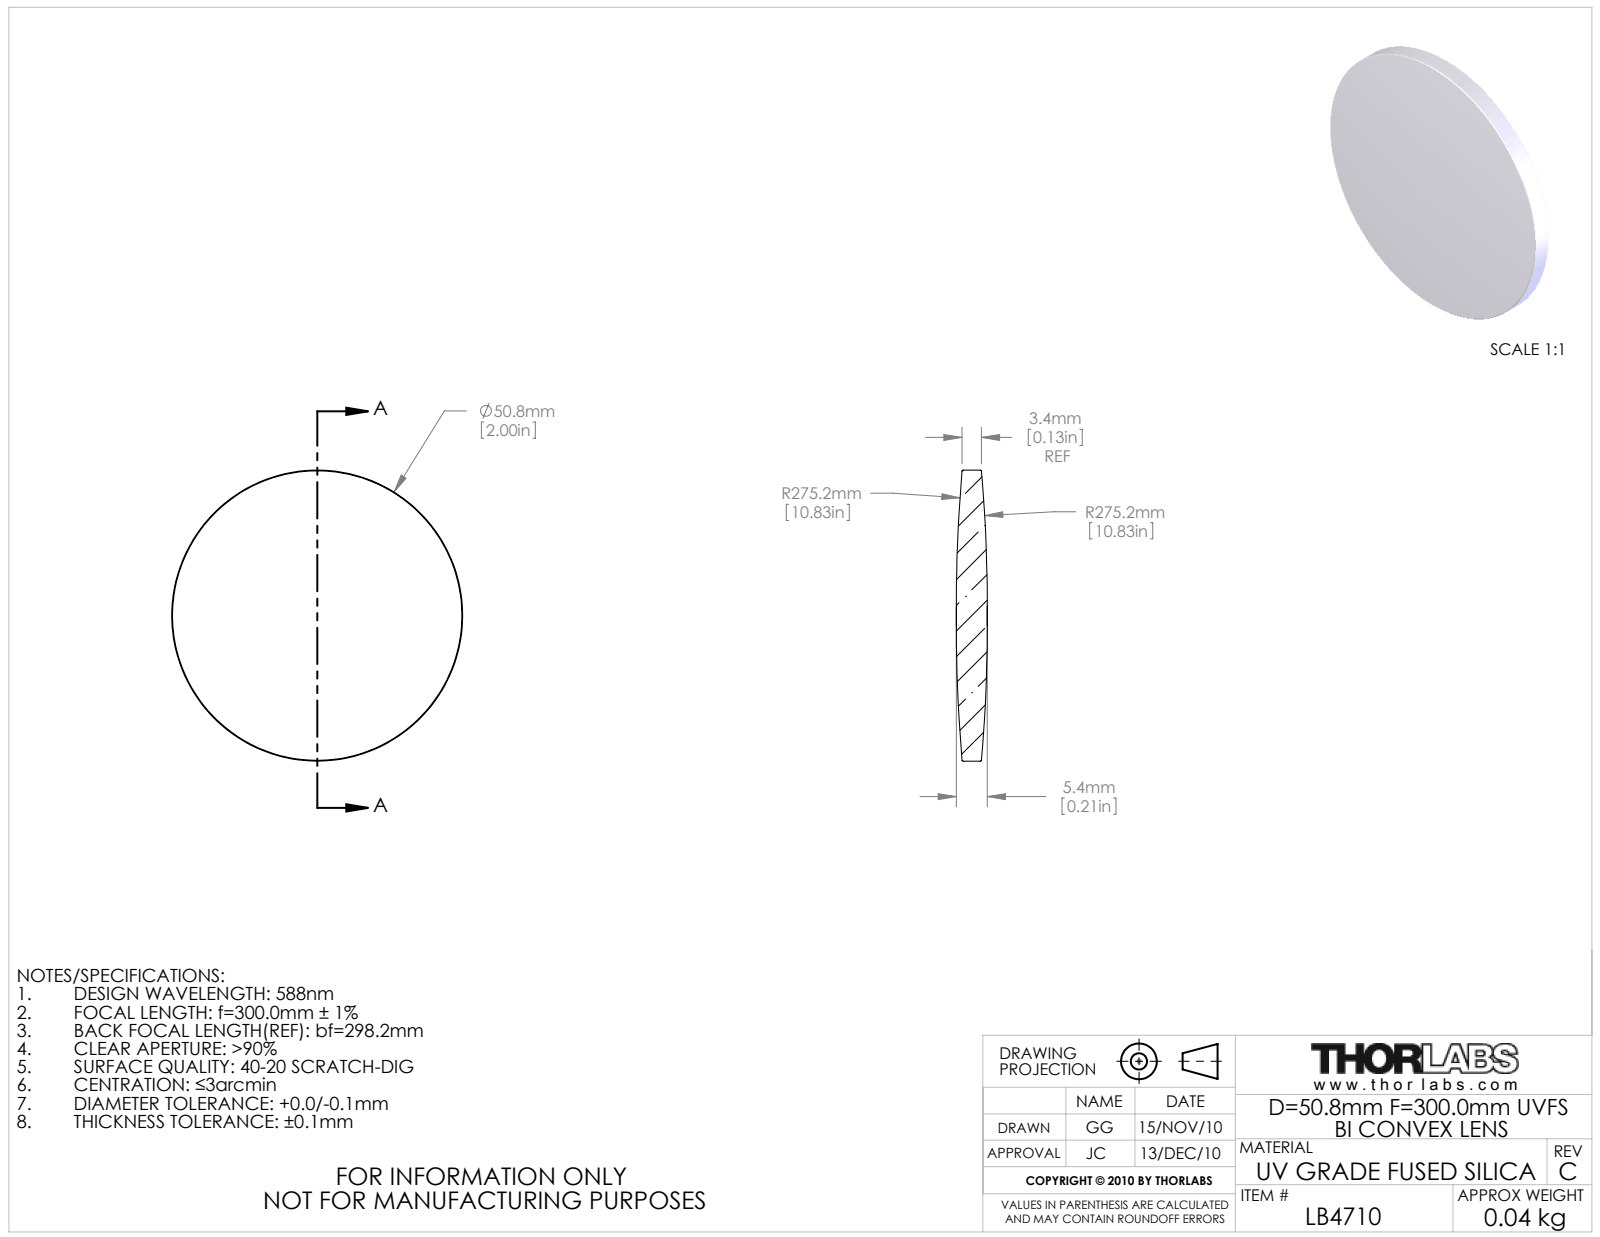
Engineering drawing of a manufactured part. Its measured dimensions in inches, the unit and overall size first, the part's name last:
Units: inches
Overall size (bounding box): 2 × 2 × 0.213
Round bosses / shafts (diameter × count): ⌀2 ×1
Volume: 0.548 in³ · Surface area: 7.09 in²
Bodies: 1 solid, 10 faces (0 planar, 2 cylindrical, 8 other)
Part name (STEP PRODUCT): 3419-E0W
STEP written by: SolidWorks 2009 (AUTOMOTIVE_DESIGN)
